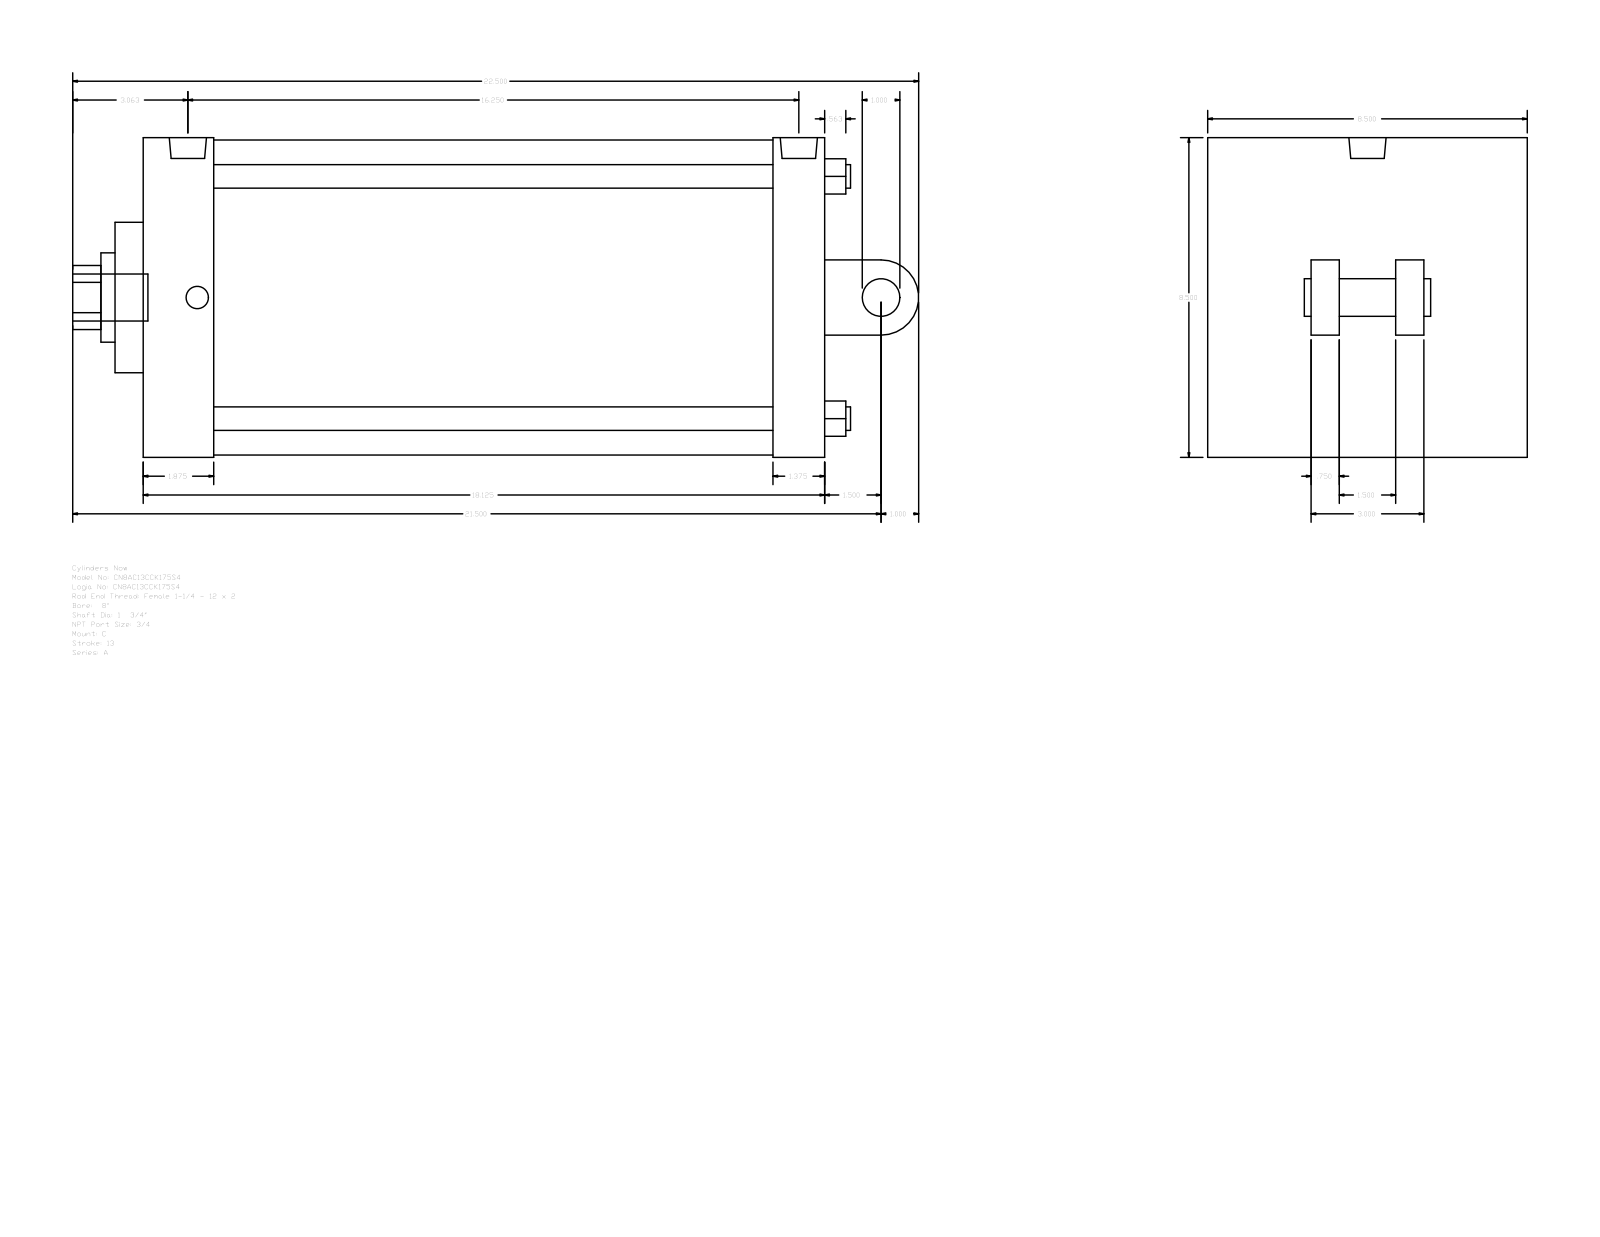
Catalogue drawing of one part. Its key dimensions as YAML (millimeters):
part_name: "A_C__0800_1.75"
step_written_by: "GSSL Pune (CONFIG_CONTROL_DESIGN)"
units: millimeters
bodies: {solids: 0, faces: 104, planar: 75, cylindrical: 29, other: 0}
overall_size: [571.5, 215.9, 215.9]
round_holes:
  - {diameter: 15.88, count: 4}
  - {diameter: 15.08, count: 2}
  - {diameter: 25.12, count: 1}
  - {diameter: 44.45, count: 1}
  - {diameter: 60.33, count: 1}
  - {diameter: 212.72, count: 1}
round_bosses_or_shafts:
  - {diameter: 15.08, count: 2}
  - {diameter: 31.75, count: 1}
  - {diameter: 25.4, count: 1}
  - {diameter: 25.12, count: 1}
partial_cylinders:
  - {radius: 21.63, count: 1}
  - {radius: 25.4, count: 1}
face_to_face_distances: [460.38, 215.9, 19.05, 57.15, 47.63, 412.75, 425.45, 377.82, 34.93, 88.9]
hole_center_spacings: [115.67, 163.58, 231.34, 6.35]
